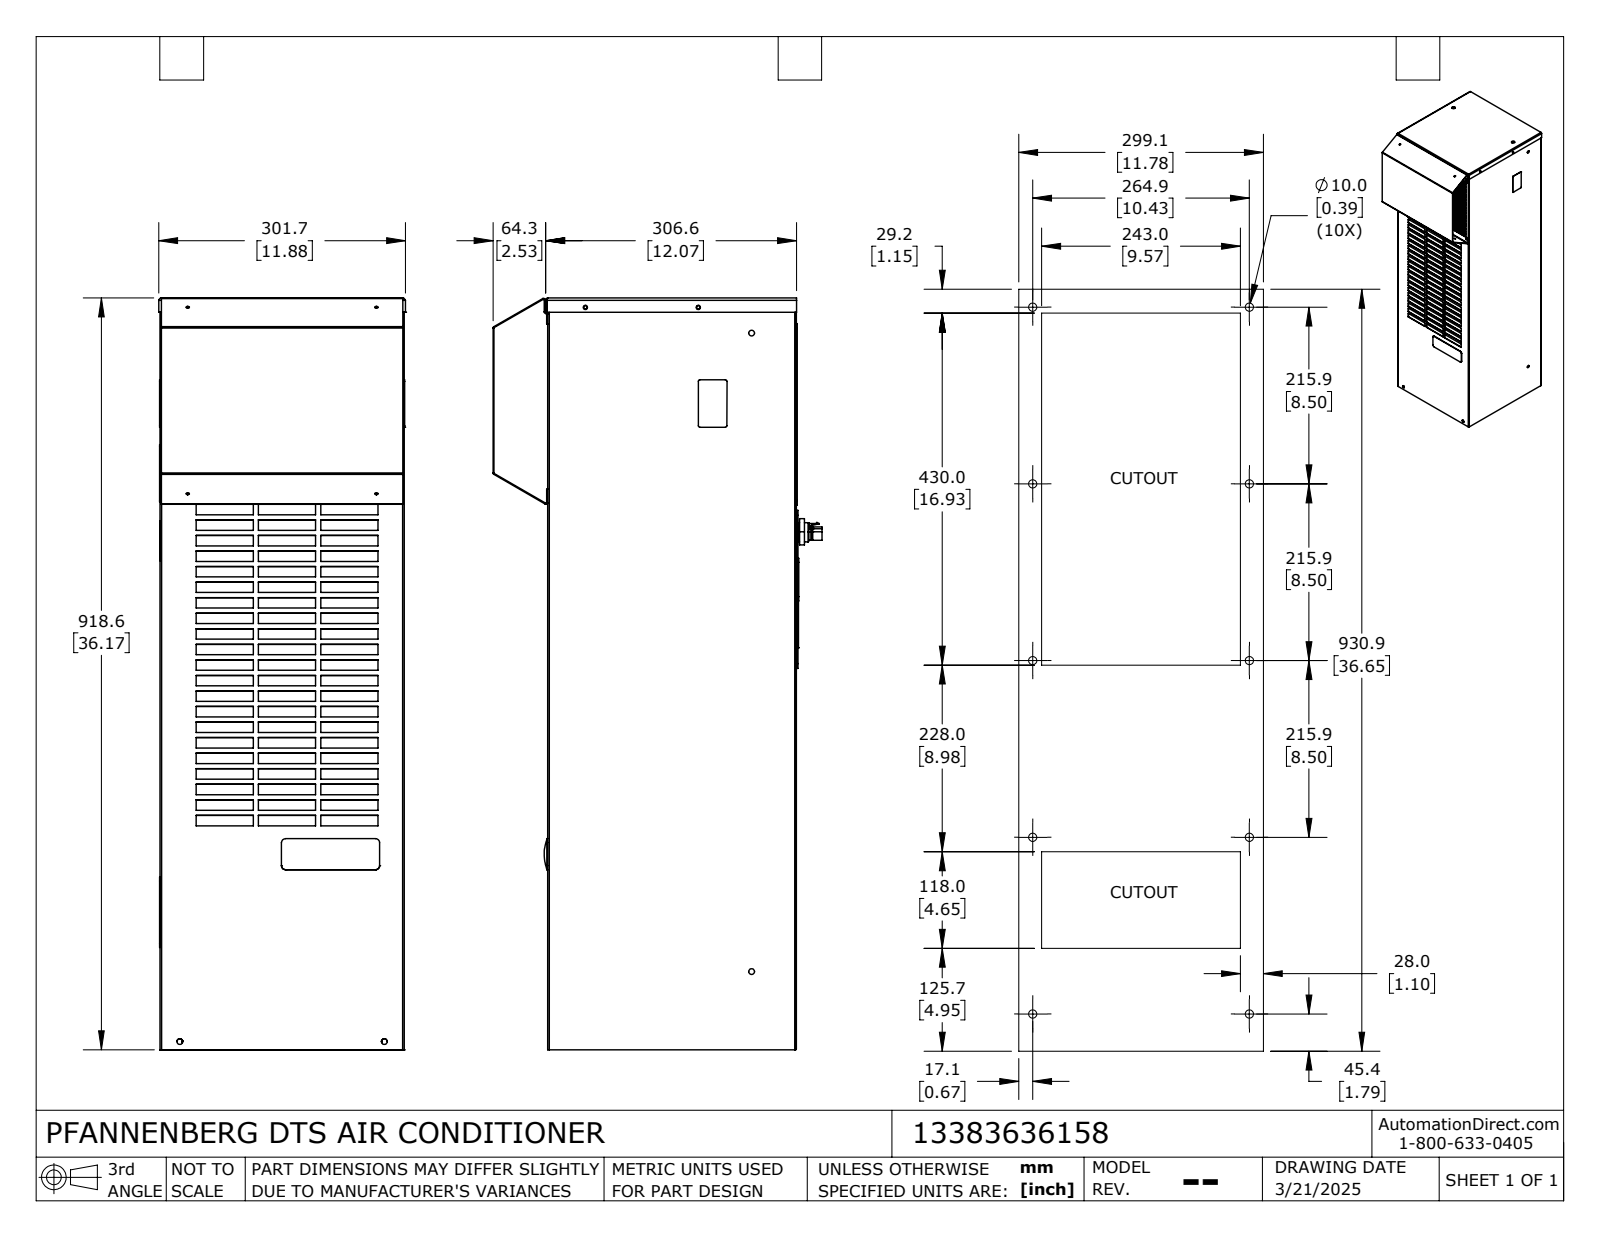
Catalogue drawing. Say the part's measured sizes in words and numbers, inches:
The part is named "13383636158_Default". Its 3-D file was written by "SolidWorks 2024 (CONFIG_CONTROL_DESIGN)". It is 1 solid with 1788 faces: 1242 planar, 493 cylindrical and 53 other. Overall it measures 36.166 by 15.829 by 11.878 inches. Its volume is 4 957 cubic inches and its surface area 4 043 square inches. Round holes: 35 of diameter 0.165, 10 of diameter 0.189, 6 of diameter 0.276, 5 of diameter 0.169, 5 of diameter 0.209, 4 of diameter 0.122, 4 of diameter 0.161, 2 of diameter 0.17, 2 of diameter 0.203, 2 of diameter 0.394, 2 of diameter 0.945, 1 of diameter 0.315. Round bosses or shafts: 4 of diameter 0.079, 2 of diameter 0.866, 1 of diameter 1.378, 1 of diameter 0.906. Partial cylindrical surfaces (rounded edges, fillets, slot ends): 112 of radius 0.125, 19 of radius 0.031, 12 of radius 0.079, 12 of radius 0.197, 10 of radius 0.087, 10 of radius 0.236, 8 of radius 0.076, 4 of radius 0.078. The main face-to-face distances are 11.812, 11.752, 0.045, 11.843, 0.031, 11.888, 0.076, 0.056, 0.027, 11.839. The hole center spacings are 0.244, 0.294, 0.294, 0.294, 0.454, 0.488, 1.496, 6.937.
